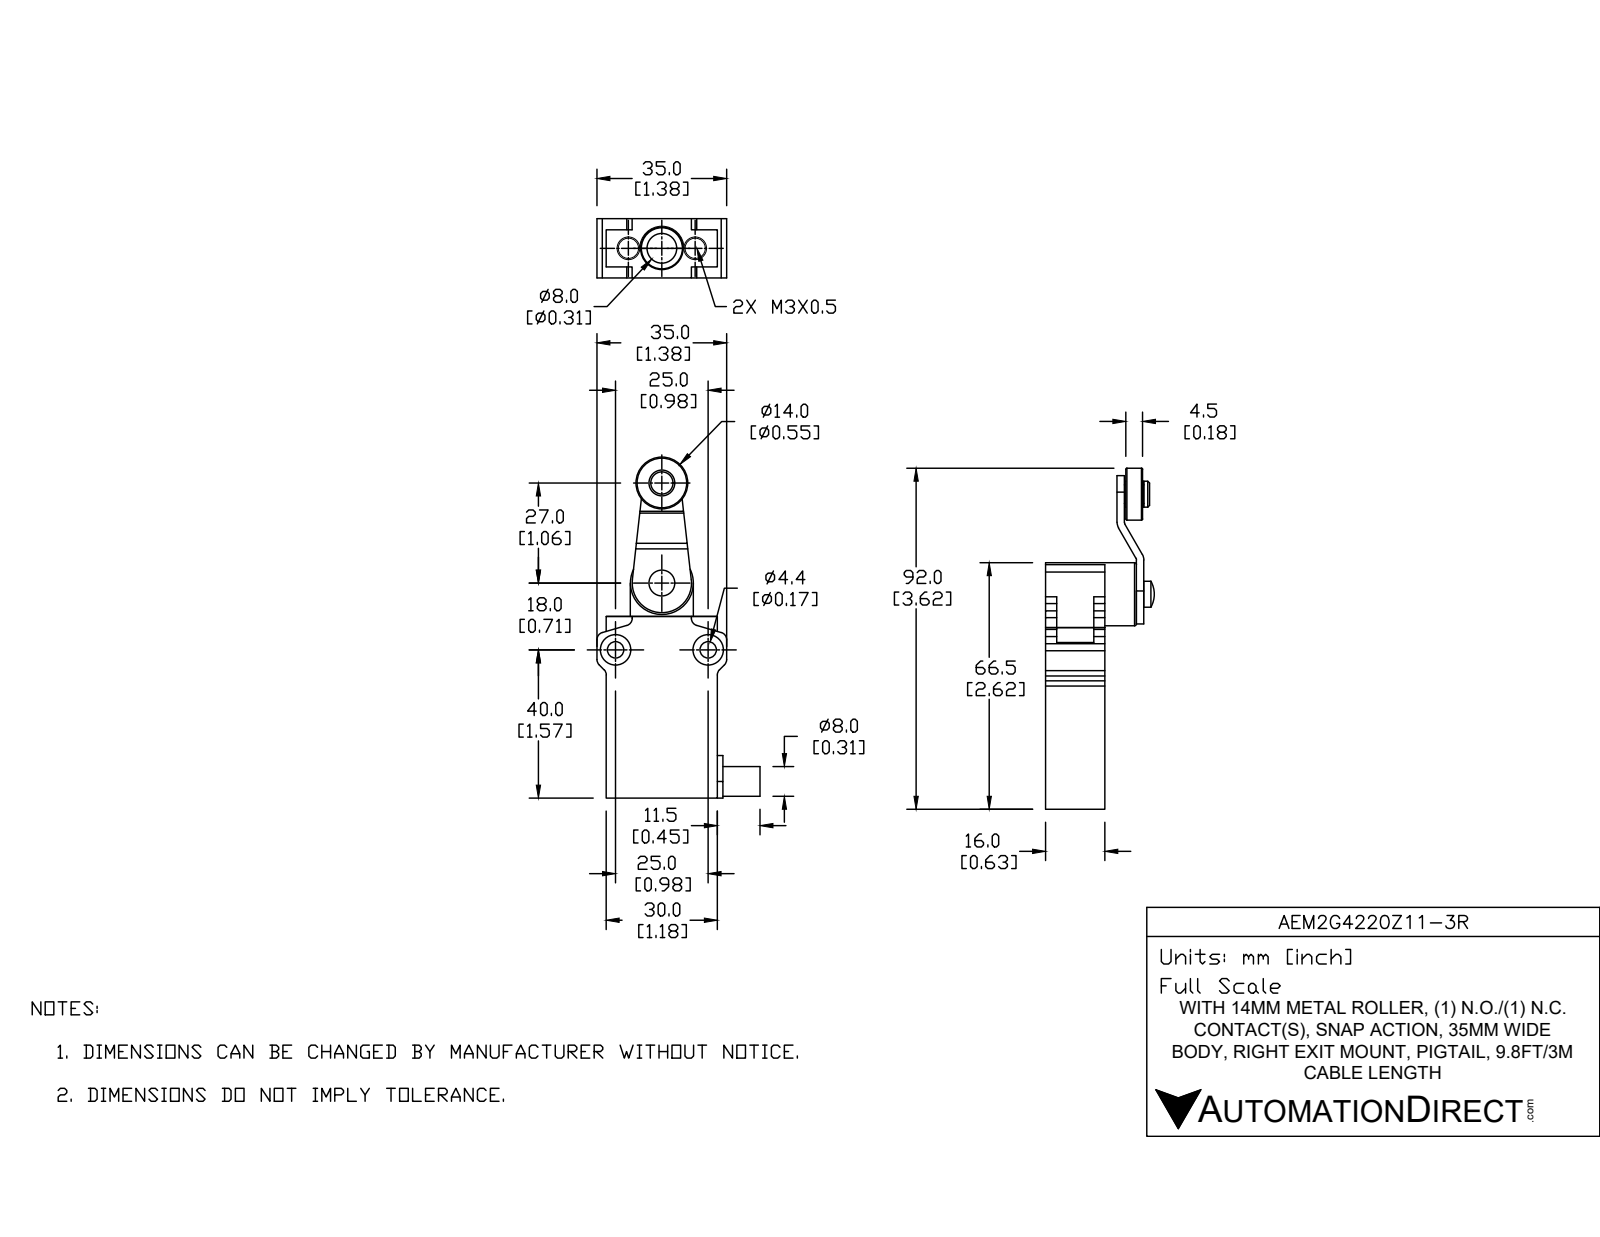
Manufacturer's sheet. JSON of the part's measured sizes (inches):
{"part_name": "AEM2G4220Z11-3R", "step_written_by": "SolidWorks 2017 (AUTOMOTIVE_DESIGN)", "units": "inches", "bodies": {"solids": 7, "faces": 543, "planar": 297, "cylindrical": 73, "other": 173}, "overall_size": [3.602, 1.87, 1.26], "volume_in3": 1.855, "surface_area_in2": 17.74, "round_holes": [[0.118, 2], [0.173, 2], [0.323, 2], [0.098, 1], [0.138, 1], [0.161, 1], [0.197, 1], [0.224, 1]], "round_bosses_or_shafts": [[0.276, 2], [0.622, 1], [0.551, 1], [0.394, 1], [0.323, 1], [0.236, 1], [0.197, 1], [0.157, 1]], "partial_cylinders_radius": [[0.079, 8], [0.039, 2], [0.118, 2], [0.256, 1], [0.315, 1]], "face_to_face_distances": [0.63, 1.181, 1.929, 0.354, 0.079, 0.984, 0.28, 0.902, 0.102, 0.472], "hole_center_spacings": [0.863, 1.82, 0.748, 0.984, 1.043]}
